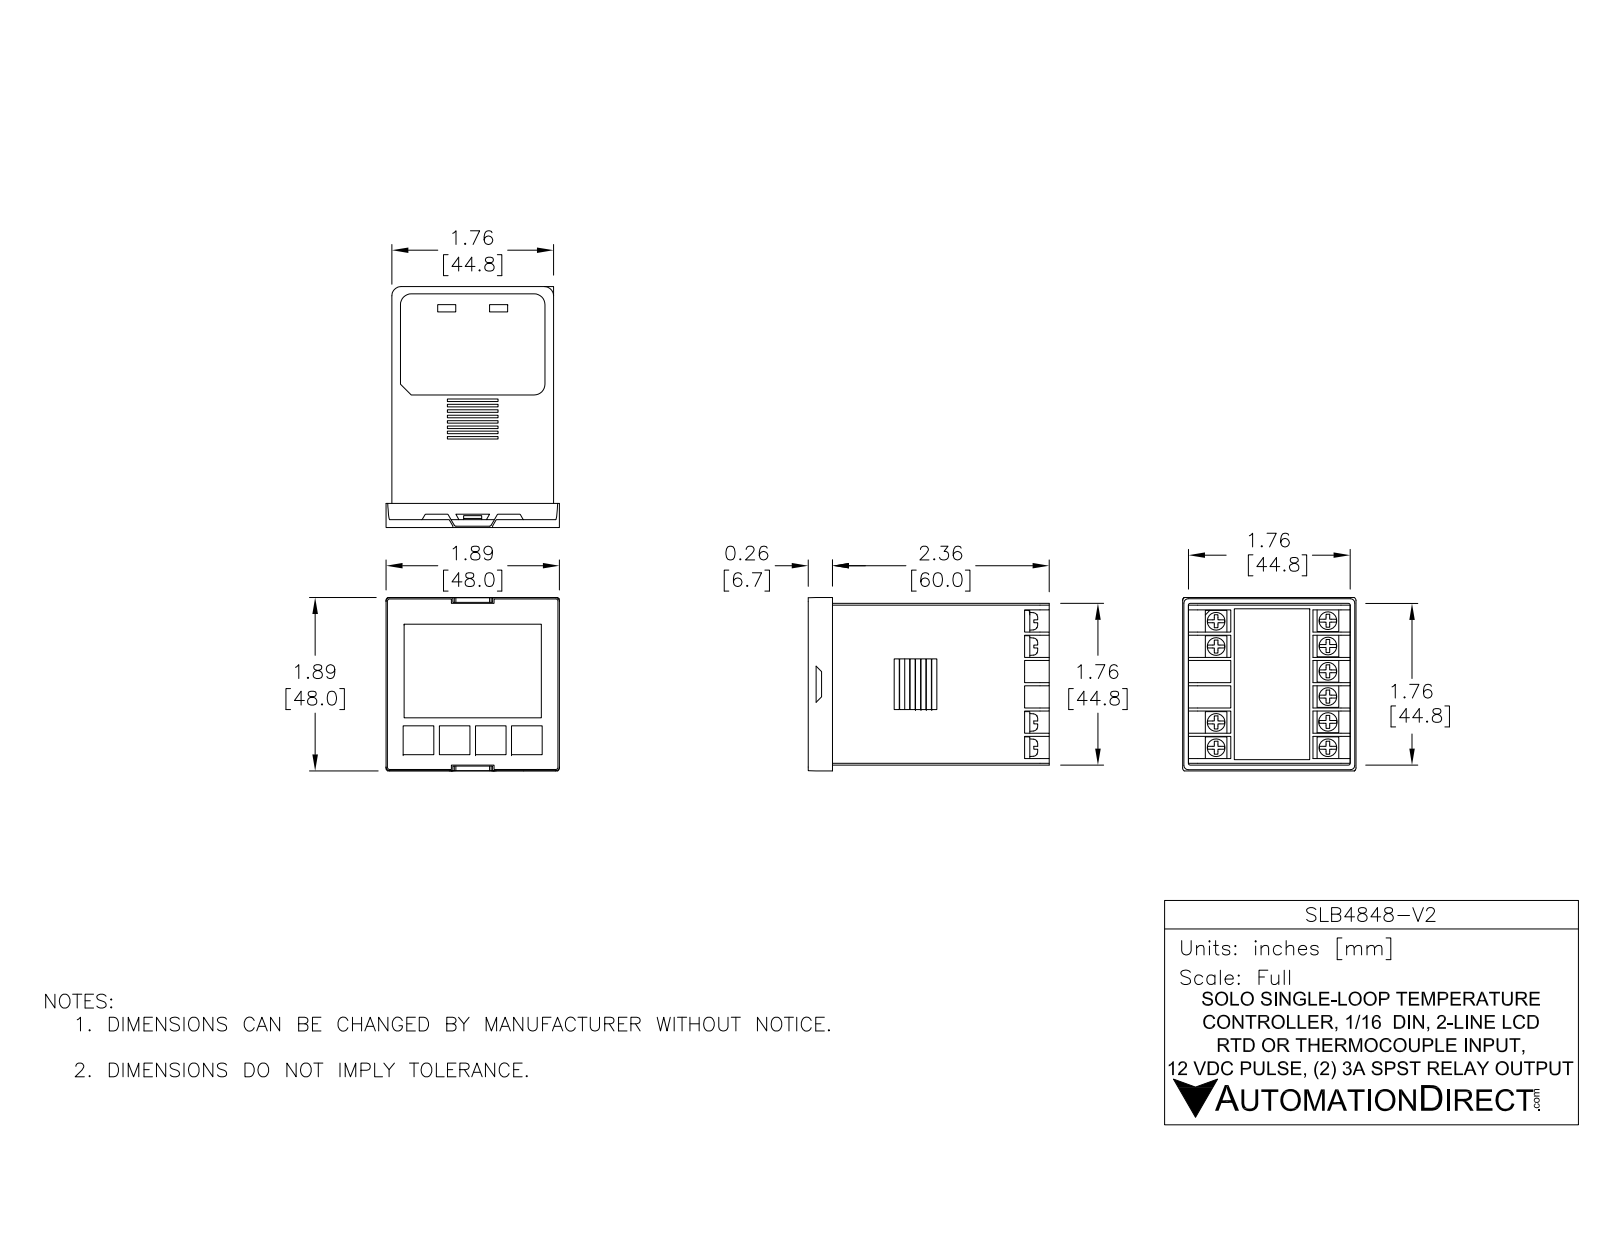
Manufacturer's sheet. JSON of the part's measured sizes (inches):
{"part_name": "SLB4848-V2", "step_written_by": "SolidWorks 2017 (AUTOMOTIVE_DESIGN)", "units": "inches", "bodies": {"solids": 8, "faces": 3493, "planar": 3222, "cylindrical": 141, "other": 130}, "overall_size": [2.628, 2.234, 1.89], "volume_in3": 7.705, "surface_area_in2": 47.25, "round_bosses_or_shafts": [[0.21, 2], [0.114, 2]], "partial_cylinders_radius": [[0.006, 36], [0.008, 8], [0.02, 6], [0.039, 6], [0.024, 4], [0.04, 4], [0.063, 4], [0.157, 4]], "face_to_face_distances": [1.762, 0.049, 1.813, 0.016, 1.746, 0.05, 1.763, 1.764, 1.763, 1.812]}
